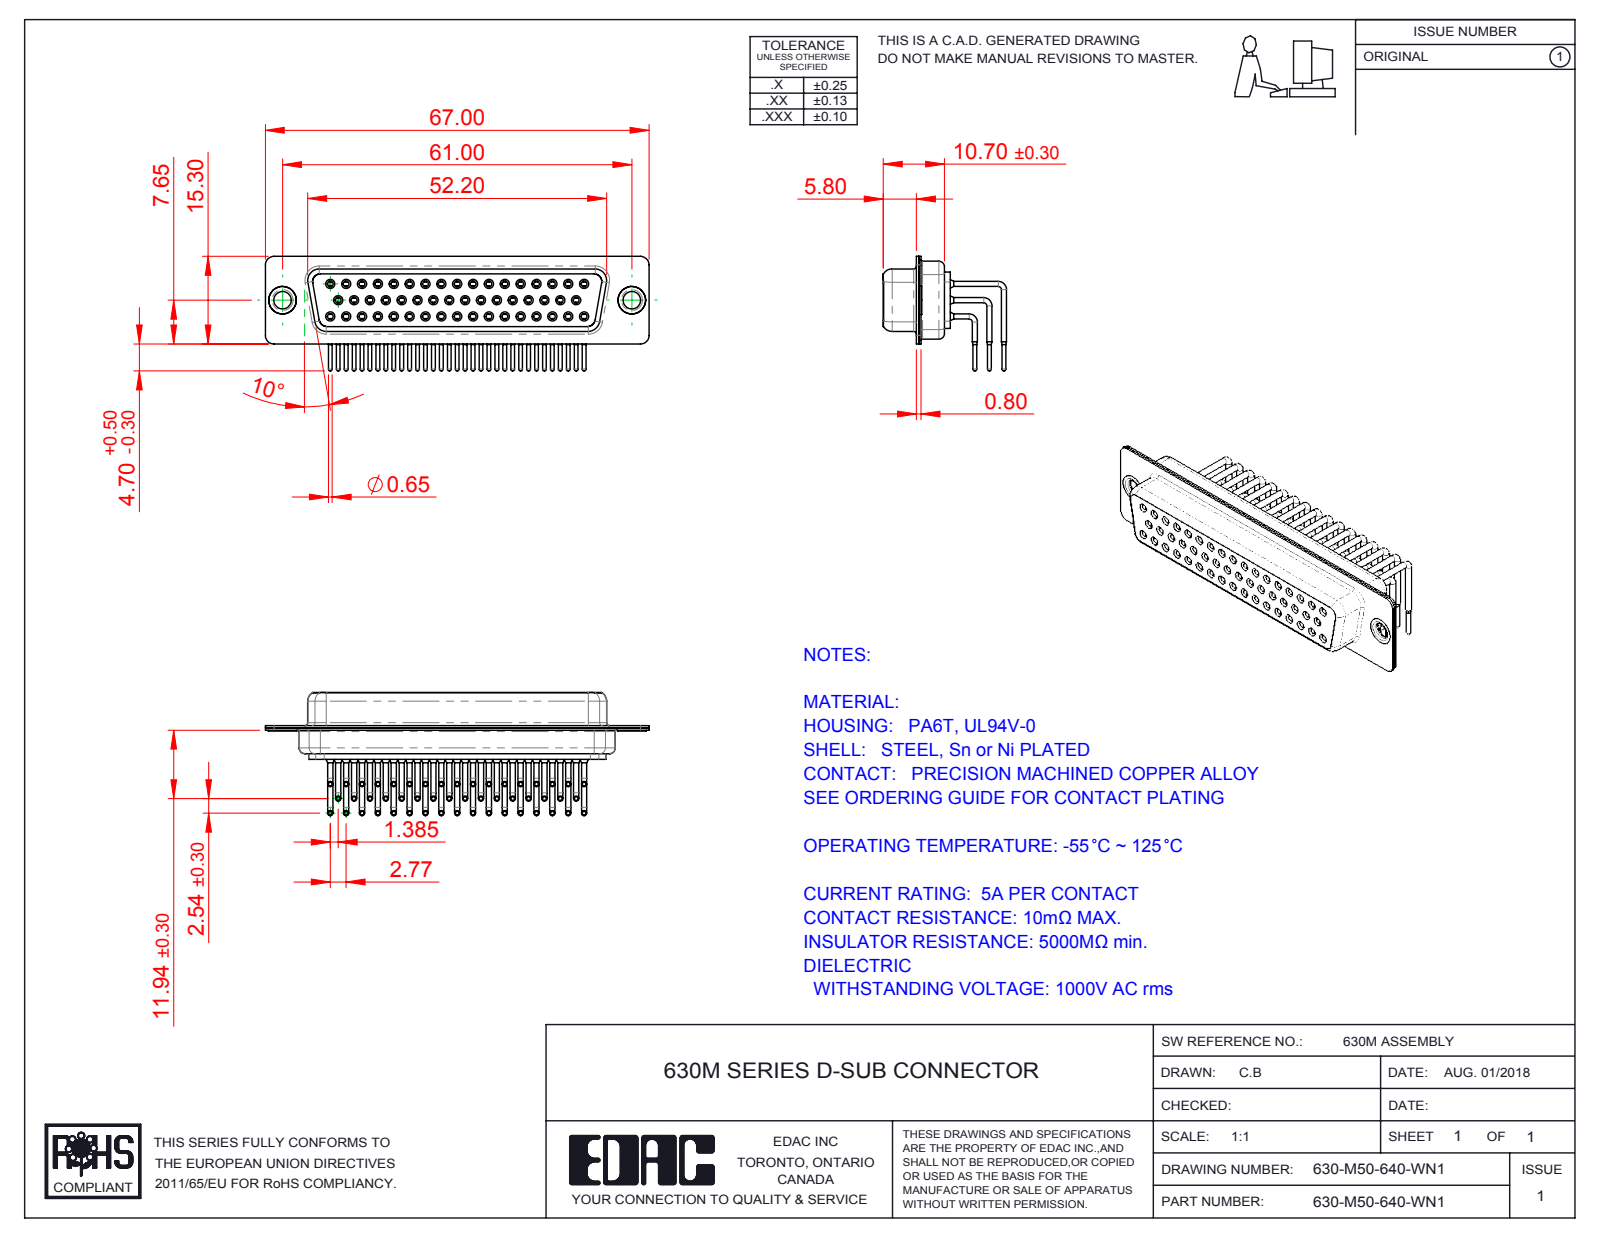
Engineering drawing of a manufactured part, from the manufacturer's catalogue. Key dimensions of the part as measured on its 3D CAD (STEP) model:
Part name (STEP PRODUCT): 630M Contact Row 2_50 Contacts; 630M Shell Front_50 Contacts; 630-M50-640-WN1; 630M Thru Hole Rivet (+4 more)
STEP written by: SolidWorks 2016 (CONFIG_CONTROL_DESIGN)
Units: millimetres
Bodies: 55 solids, 2903 faces (817 planar, 1271 cylindrical, 815 other)
Overall size (bounding box): 67 × 21.53 × 20
Volume: 6 941 mm³ · Surface area: 16 414 mm²
Round holes (diameter × count): ⌀1 ×50, ⌀1.1 ×50, ⌀1.7 ×50, ⌀1.8 ×50, ⌀2 ×50, ⌀3.05 ×2, ⌀4 ×2, ⌀4.8 ×2
Round bosses / shafts (diameter × count): ⌀0.9 ×100, ⌀1.6 ×50, ⌀1.5 ×50, ⌀0.65 ×50, ⌀5 ×2, ⌀4.9 ×2, ⌀3.55 ×2
Partial cylindrical surfaces — rounded edges, fillets, slot ends (radius × count): R1.5 ×16, R2 ×12, R1.35 ×8, R1.6 ×8, R0.25 ×4, R0.5 ×4, R0.6 ×4, R0.65 ×4
Main face-to-face distances: 0.4, 1.35, 11.85, 0.85, 2.2, 5.5, 12.25, 5.9, 10.5, 10.05
Hole centre spacings: 2.77, 3.16, 5.54, 8.31, 11.08, 13.85, 16.62, 19.39
